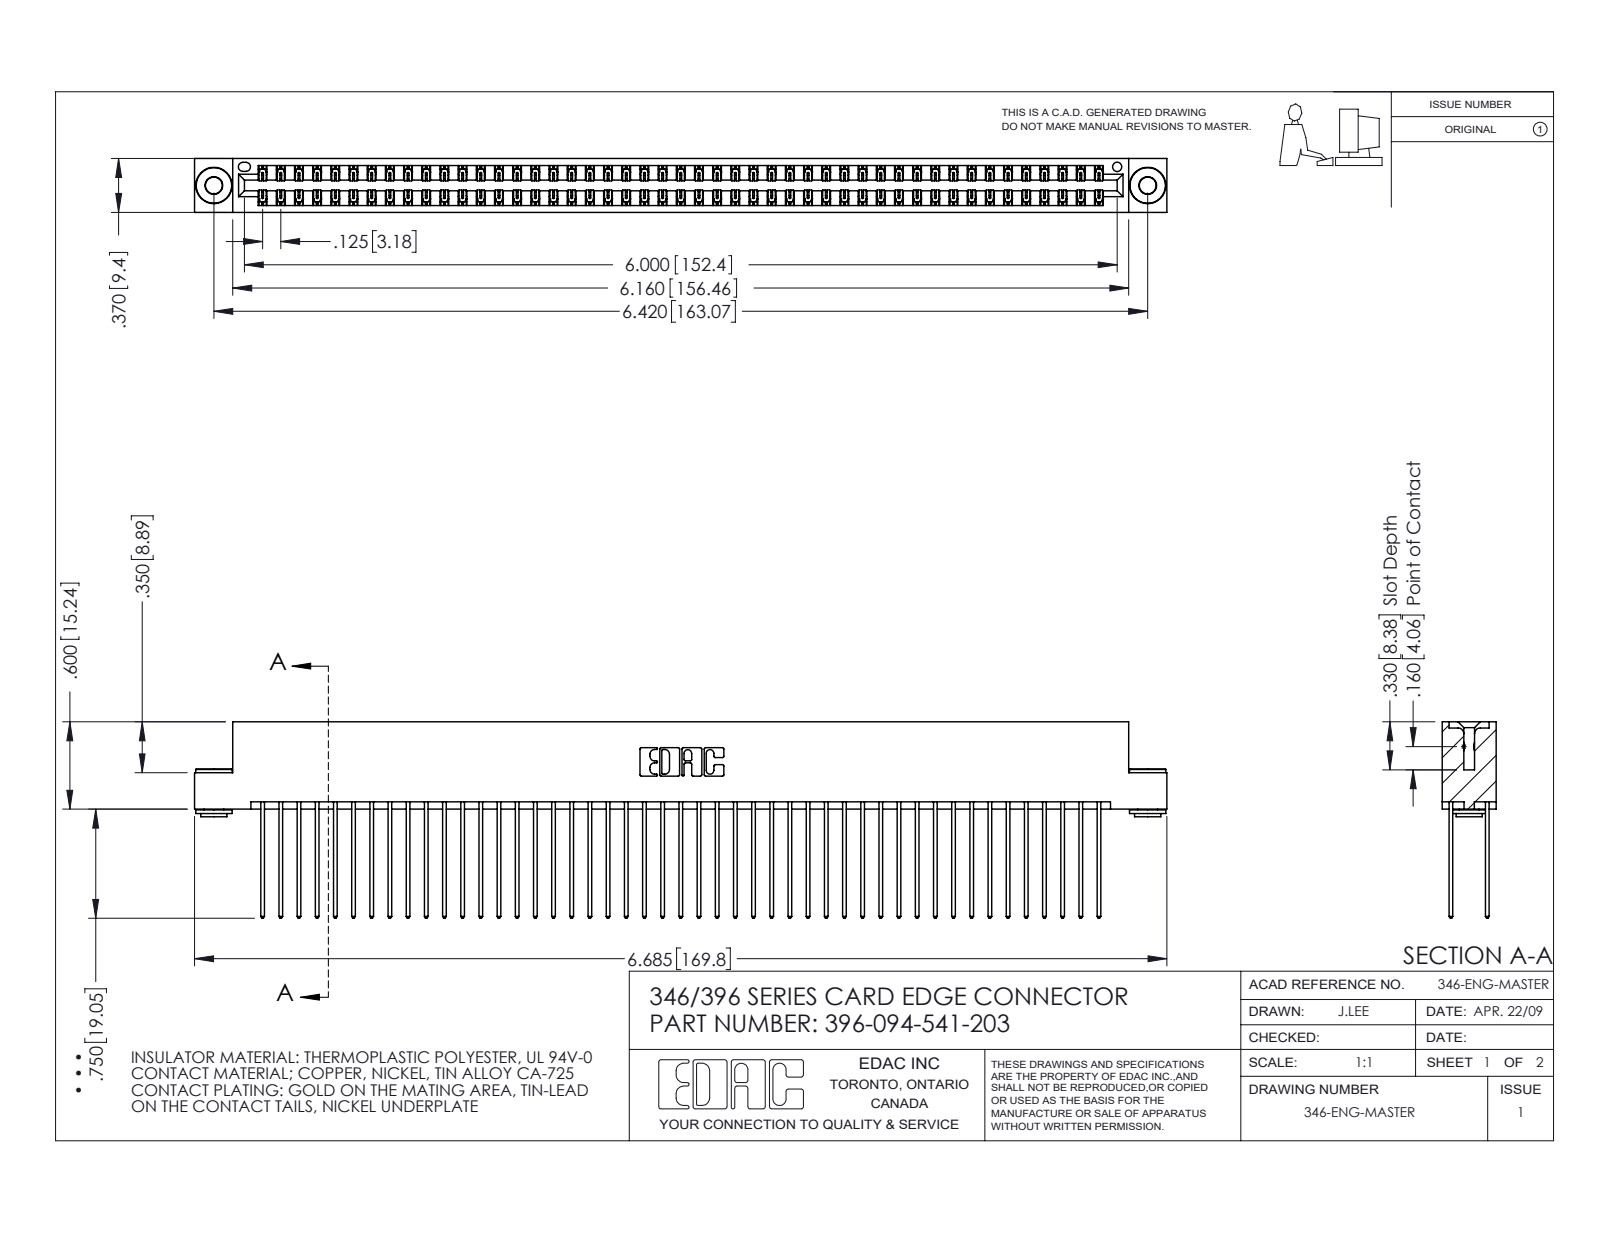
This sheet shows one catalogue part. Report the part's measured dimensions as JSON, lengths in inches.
{"part_name": "345-250-002_345-250-002-102; 346 Part_Flush Mounting Lugs - 0.156 Dia-TH; 396-094-541-203; 345-292-001_345-293-141", "step_written_by": "SolidWorks 2016 (CONFIG_CONTROL_DESIGN)", "units": "inches", "bodies": {"solids": 97, "faces": 5048, "planar": 3376, "cylindrical": 1664, "other": 8}, "overall_size": [6.685, 1.35, 0.37], "volume_in3": 1.047, "surface_area_in2": 41.01, "round_holes": [[0.116, 2], [0.156, 2], [0.064, 1]], "round_bosses_or_shafts": [[0.25, 2], [0.18, 2], [0.136, 2]], "partial_cylinders_radius": [[0.006, 141], [0.01, 94], [0.01, 22], [0.007, 6], [0.031, 6], [0.026, 3], [0.014, 2], [0.022, 2]], "face_to_face_distances": [0.048, 0.322, 0.25, 0.025, 0.072, 0.298, 0.37, 0.275, 0.225, 0.148], "hole_center_spacings": [0.246, 6.211, 6.42]}
